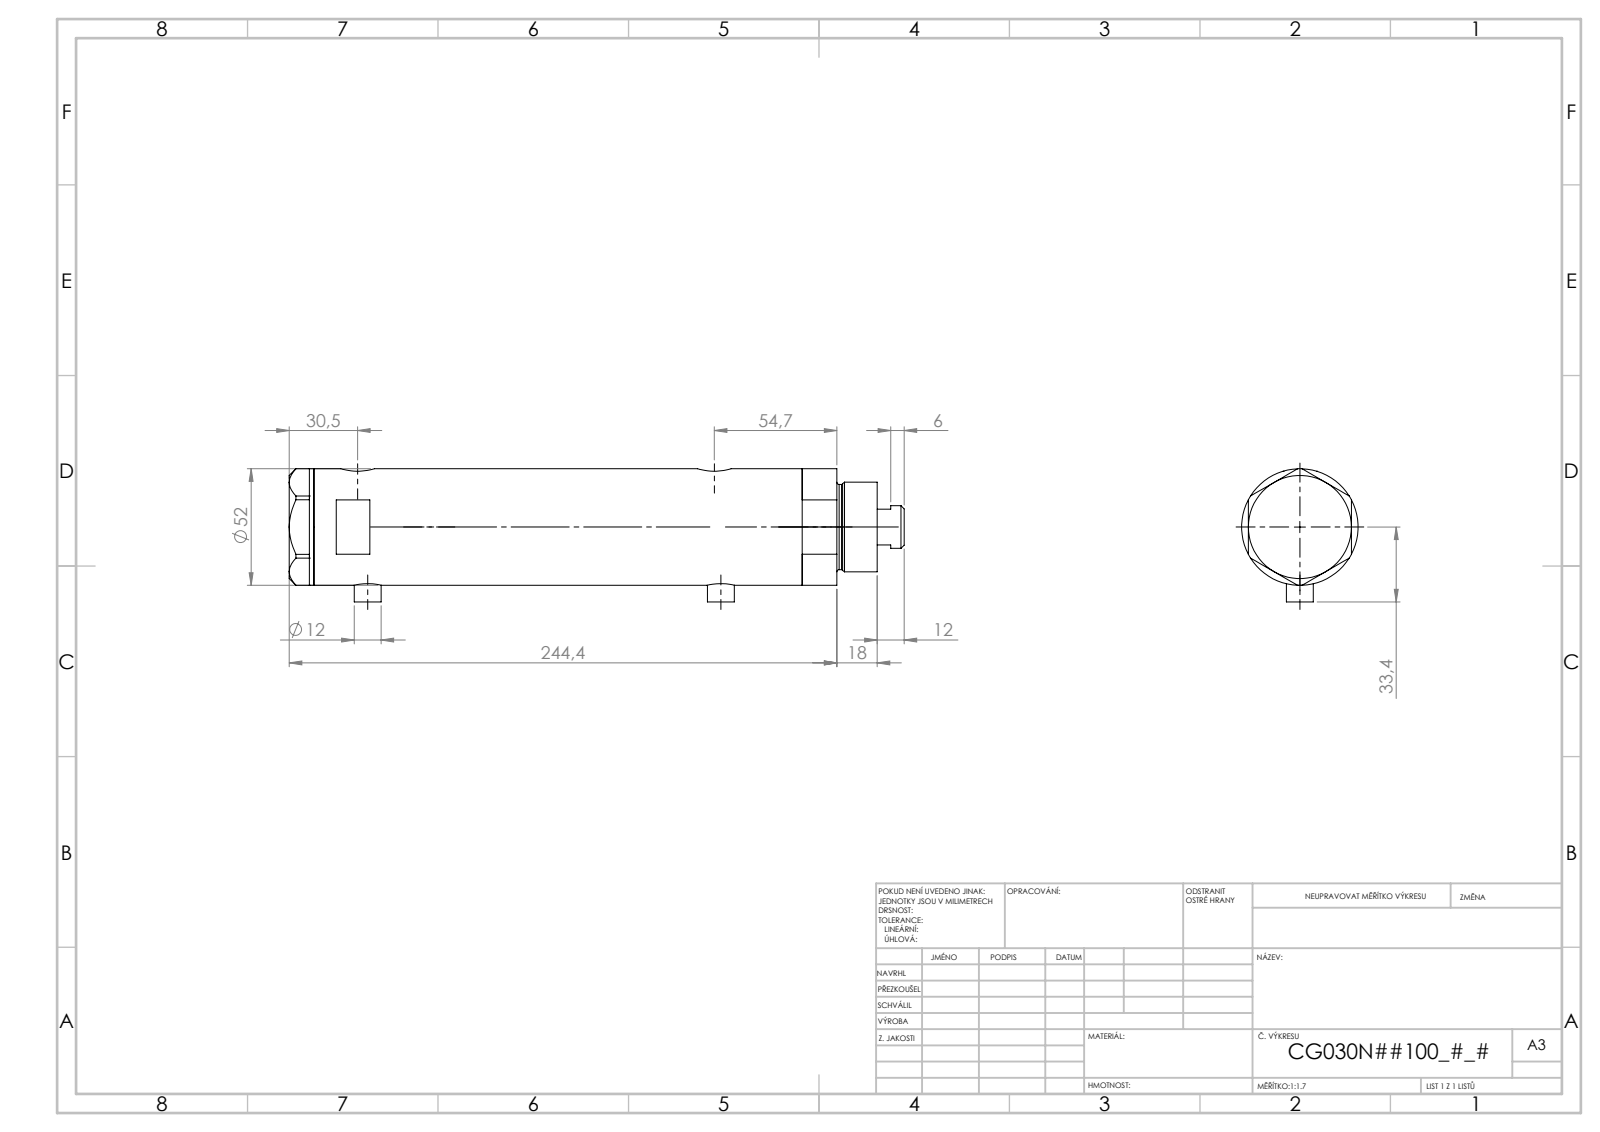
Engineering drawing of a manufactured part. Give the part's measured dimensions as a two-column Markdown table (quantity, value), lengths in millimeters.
| quantity | value |
| --- | --- |
| part name | V270CG_FRONT; V270CG_MIDDLE; V270CG_VC; V270CG_BACK |
| STEP written by | SolidWorks 2019 (CONFIG_CONTROL_DESIGN) |
| units | millimeters |
| bodies | 4 solids, 140 faces (67 planar, 53 cylindrical, 20 other) |
| overall size | 249.02 × 53.1 × 52 |
| volume | 440 620 mm³ |
| surface area | 97 134 mm² |
| round holes (diameter × count) | 5 × 2, 9.73 × 2, 12.5 × 2, 15 × 2, 6.5 × 1, 20 × 1, 21.5 × 1, 30 × 1, 33 × 1, 44 × 1 |
| round bosses / shafts (diameter × count) | 12 × 2, 52 × 1, 40 × 1, 38 × 1, 19 × 1 |
| main face-to-face distances | 153.54, 23.8, 129.74, 11, 34.8, 164.54, 46, 200.94, 189.94, 166.14 |
| hole center spacings | 2.9, 4.5, 126.75, 129.65, 131.25, 134.15, 2.89, 2.91 |
